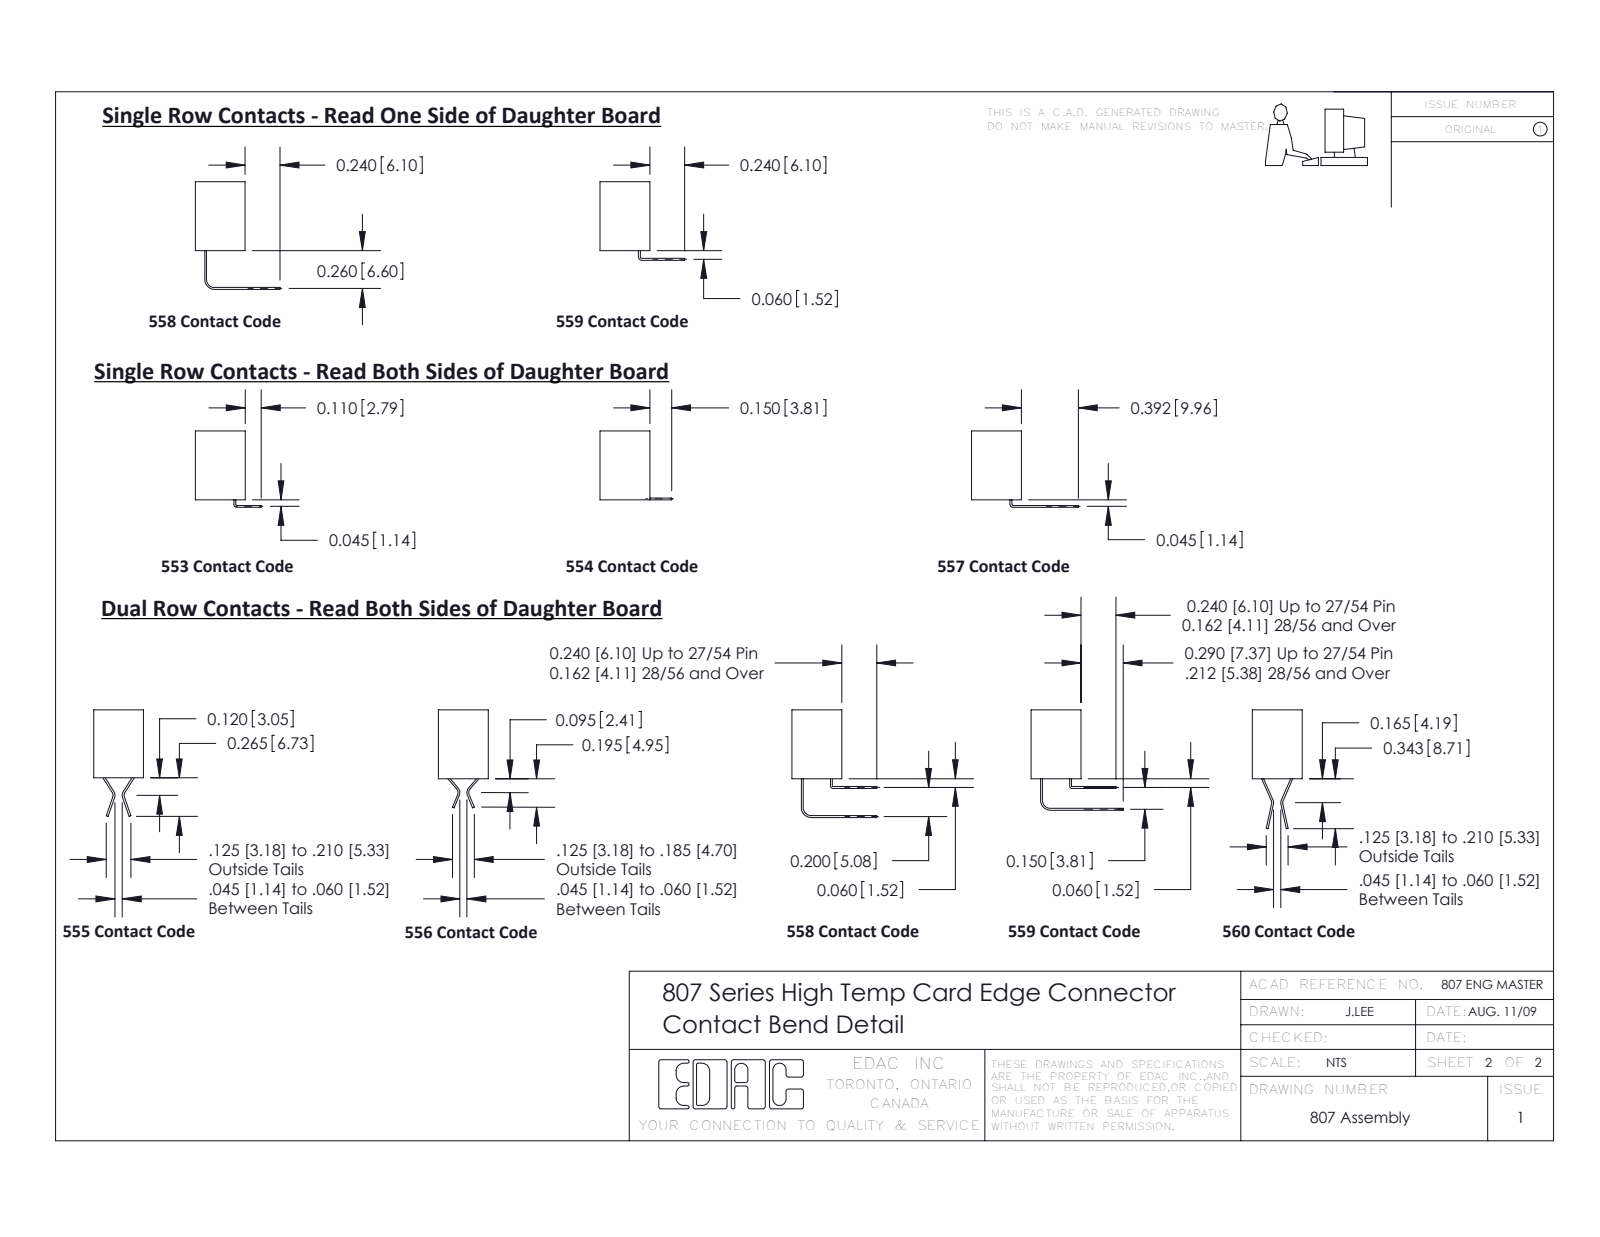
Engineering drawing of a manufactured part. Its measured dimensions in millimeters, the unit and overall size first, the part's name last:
Units: millimetres
Overall size (bounding box): 74.5 × 18.7 × 8.7
Round holes (diameter × count): ⌀2.3 ×2, ⌀3.2 ×2, ⌀4 ×2
Round bosses / shafts (diameter × count): ⌀3.9 ×2
Partial cylindrical surfaces — rounded edges, fillets, slot ends (radius × count): R0.5 ×45, R0.8 ×26, R1.6 ×26, R0.3 ×22, R0.2 ×6, R0.8 ×6, R0.7 ×3, R0.3 ×2
Main face-to-face distances: 8.7, 0.3, 1.7, 5.1, 1.6, 7.1, 7.1, 5.5, 1.6, 4
Hole centre spacings: 66.6
Volume: 4 740 mm³ · Surface area: 7 142 mm²
Bodies: 16 solids, 1115 faces (622 planar, 449 cylindrical, 44 other)
Part name (STEP PRODUCT): 345-250-001_345-250-003-102; 307-290-001_555; 307-026-555-208; 307 Part_.156 Dia Mounting Holes
STEP written by: SolidWorks 2016 (CONFIG_CONTROL_DESIGN)
